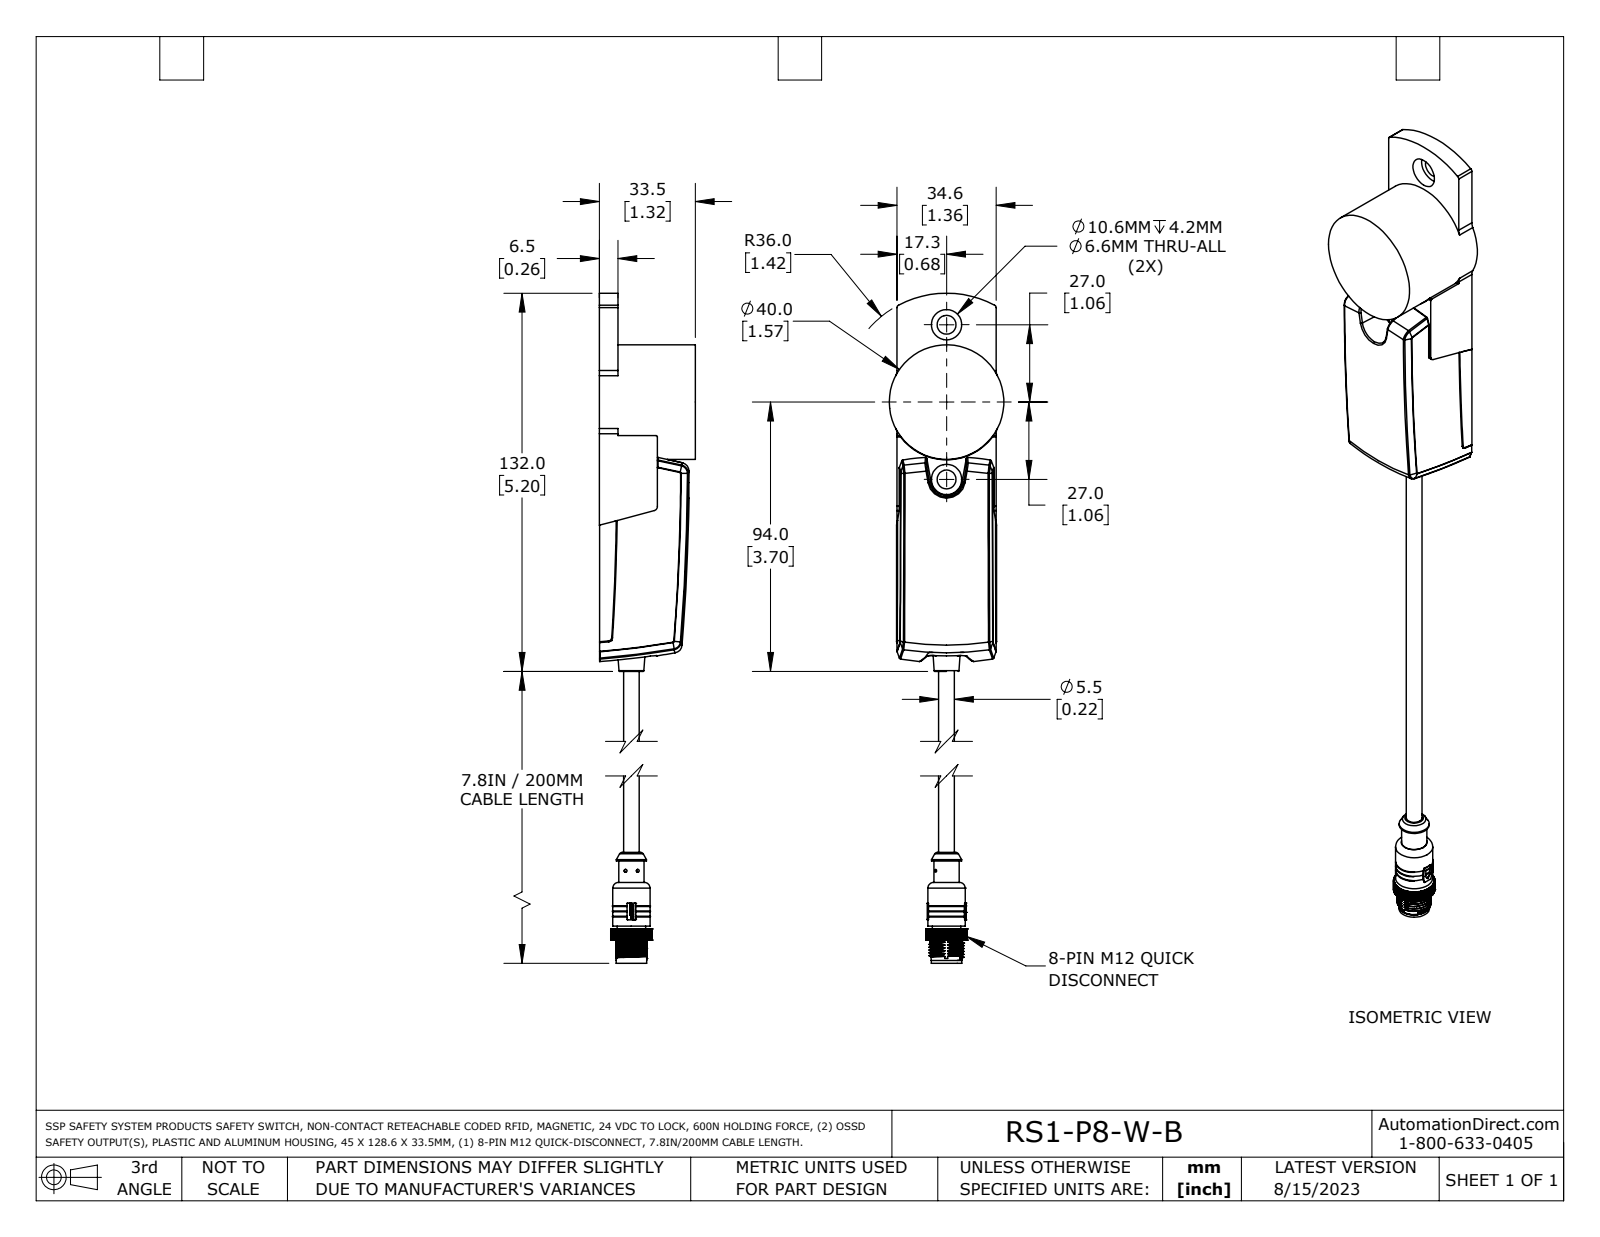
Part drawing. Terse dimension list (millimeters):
name: RS1-P8-S-B_REV2
written by: SolidWorks 2021 (AUTOMOTIVE_DESIGN)
unit: mm
bodies: 1 solid, 974 faces (561 planar, 150 cylindrical, 263 other)
size: 323.1 × 40 × 33.5
volume: 122 300 mm³; area: 25 390 mm²
holes: 2× ⌀1, 2× ⌀4.2, 2× ⌀6.6, 2× ⌀10.6, 1× ⌀2.9, 1× ⌀8.3, 1× ⌀9.5
bosses: 8× ⌀0.8, 1× ⌀40, 1× ⌀13, 1× ⌀10.7, 1× ⌀10.7, 1× ⌀10.5, 1× ⌀10, 1× ⌀9.5
rounds: 7× R0.2, 5× R0.2, 4× R0.2, 4× R4, 2× R1, 2× R800, 1× R0.5, 1× R0.6
face distances: 33.5, 33.4, 34.6, 6.5, 6.4, 27, 34.7, 34.9, 20.3, 20.2
hole spacings: 12, 15, 27, 39, 4.3, 9.3, 24, 24.3
